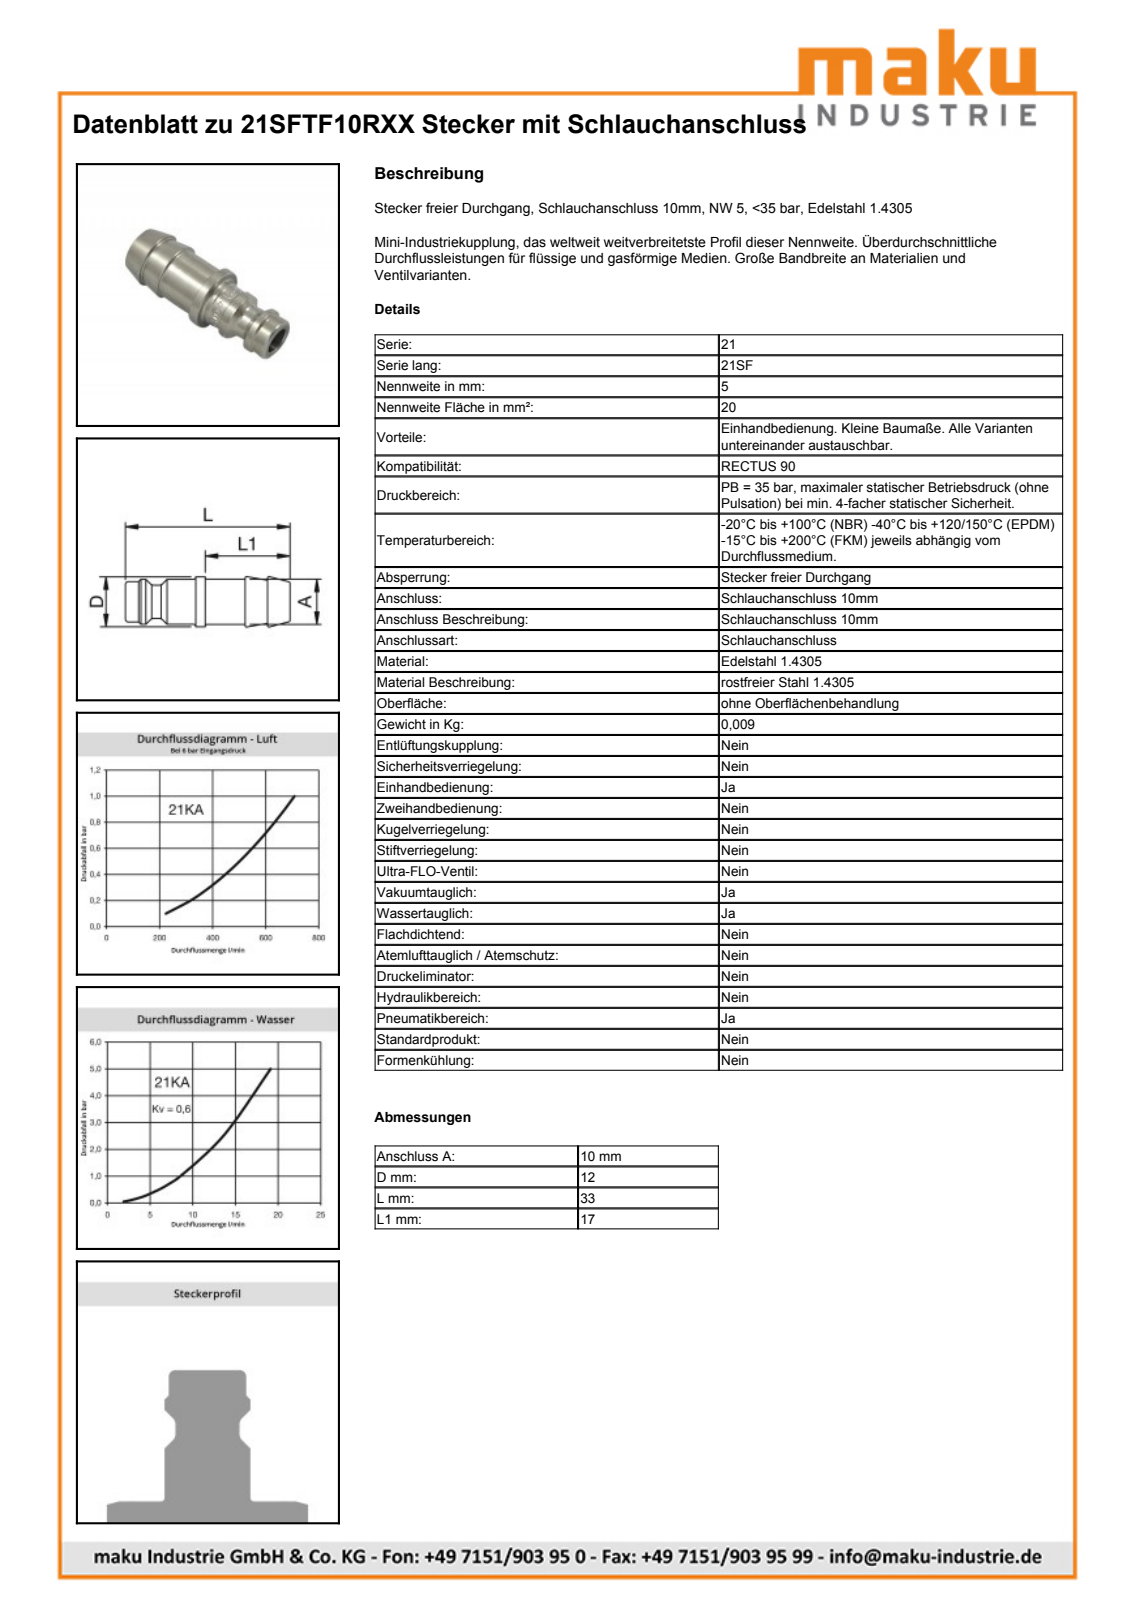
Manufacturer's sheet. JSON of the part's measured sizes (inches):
{"part_name": "D110089", "step_written_by": "Autodesk Inventor 2013 (AUTOMOTIVE_DESIGN)", "units": "inches", "bodies": {"solids": 1, "faces": 28, "planar": 6, "cylindrical": 8, "other": 14}, "overall_size": [1.299, 0.472, 0.472], "volume_in3": 0.075, "surface_area_in2": 2.855, "round_holes": [[0.195, 1], [0.315, 1]], "round_bosses_or_shafts": [[0.472, 1], [0.396, 1], [0.354, 1], [0.319, 1], [0.262, 1]], "face_to_face_distances": [0.555, 0.63, 0.075, 1.122, 0.567, 0.492, 0.177, 0.945, 0.39, 0.315]}
